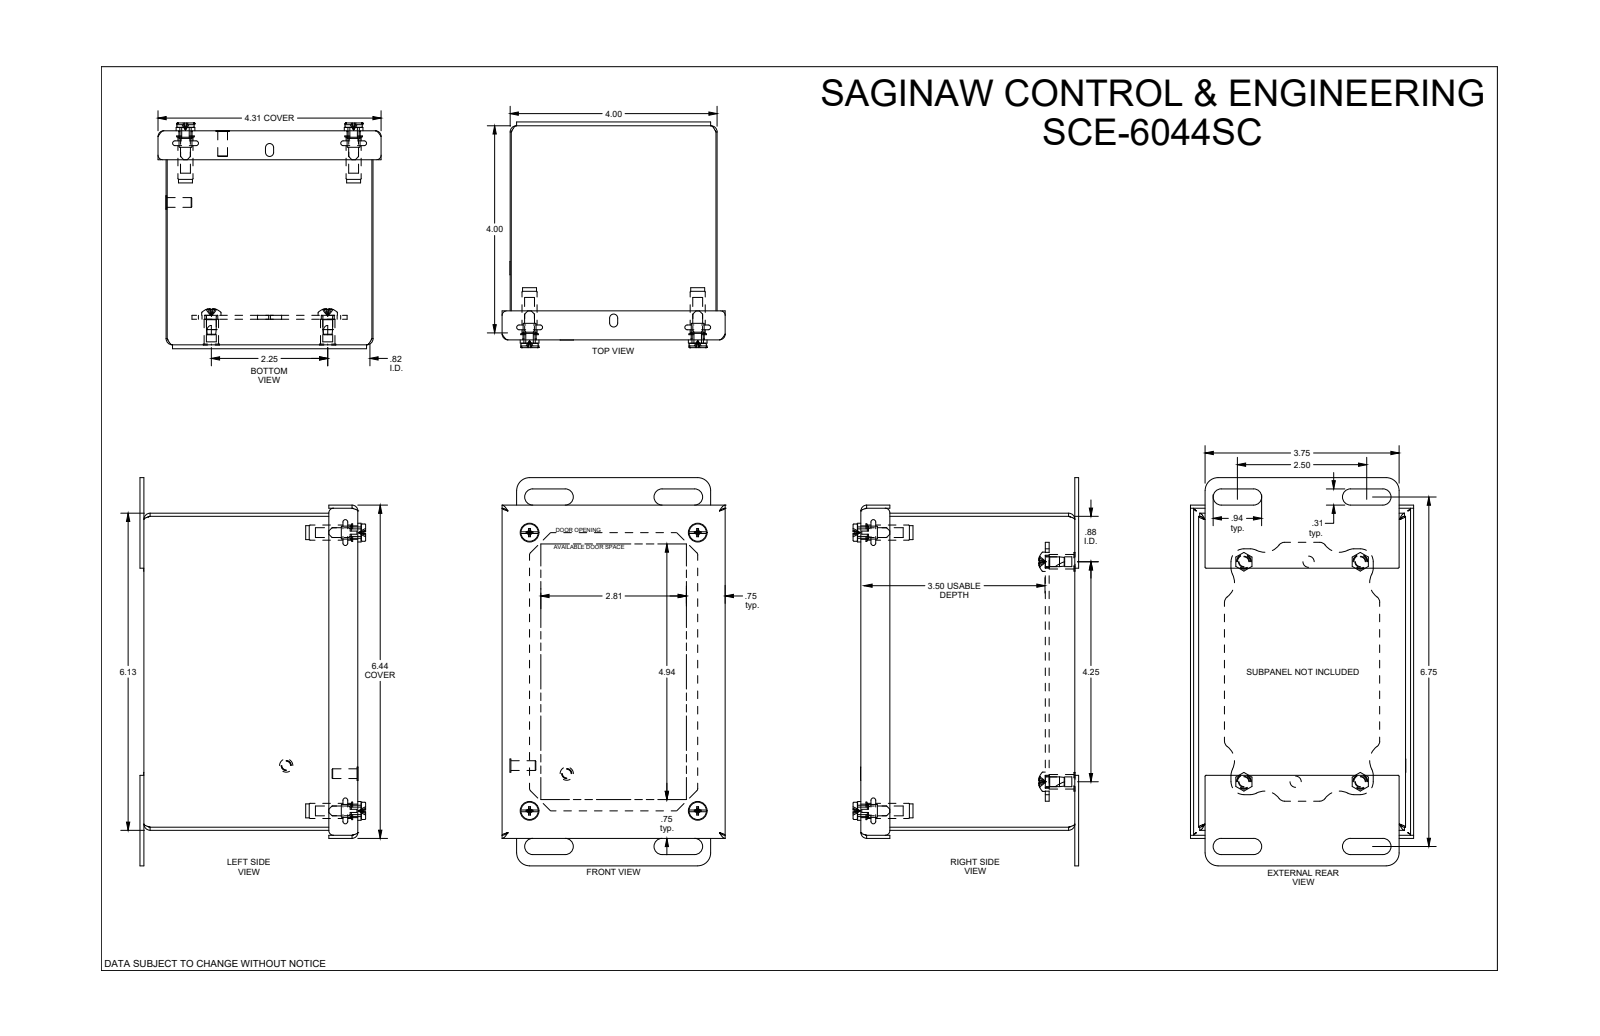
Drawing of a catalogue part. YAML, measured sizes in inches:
part_name: "SCE-6044SC"
step_written_by: "SolidWorks 2021 (AUTOMOTIVE_DESIGN)"
units: inches
bodies: {solids: 23, faces: 745, planar: 285, cylindrical: 195, other: 265}
overall_size: [7.5, 4.361, 4.313]
volume: 11.52
surface_area: 375.9
round_holes:
  - {diameter: 0.25, count: 8}
  - {diameter: 0.19, count: 4}
  - {diameter: 0.22, count: 4}
  - {diameter: 0.266, count: 4}
  - {diameter: 0.281, count: 4}
  - {diameter: 0.317, count: 4}
  - {diameter: 0.218, count: 2}
  - {diameter: 0.187, count: 1}
  - {diameter: 0.193, count: 1}
round_bosses_or_shafts:
  - {diameter: 0.188, count: 9}
  - {diameter: 0.437, count: 4}
  - {diameter: 0.373, count: 4}
  - {diameter: 0.362, count: 4}
  - {diameter: 0.34, count: 4}
  - {diameter: 0.334, count: 4}
  - {diameter: 0.292, count: 4}
  - {diameter: 0.27, count: 4}
partial_cylinders:
  - {radius: 0.125, count: 16}
  - {radius: 0.25, count: 16}
  - {radius: 0.06, count: 12}
  - {radius: 0.005, count: 8}
  - {radius: 0.05, count: 8}
  - {radius: 0.063, count: 8}
  - {radius: 0.156, count: 8}
  - {radius: 0.255, count: 8}
face_to_face_distances: [0.06, 3.94, 4.075, 6.065, 3.88, 4, 4.135, 4.015, 3.505, 0.075]
hole_center_spacings: [2.807, 6.281, 4.839, 5.543, 0.752, 5.375, 0.753, 3.25]
